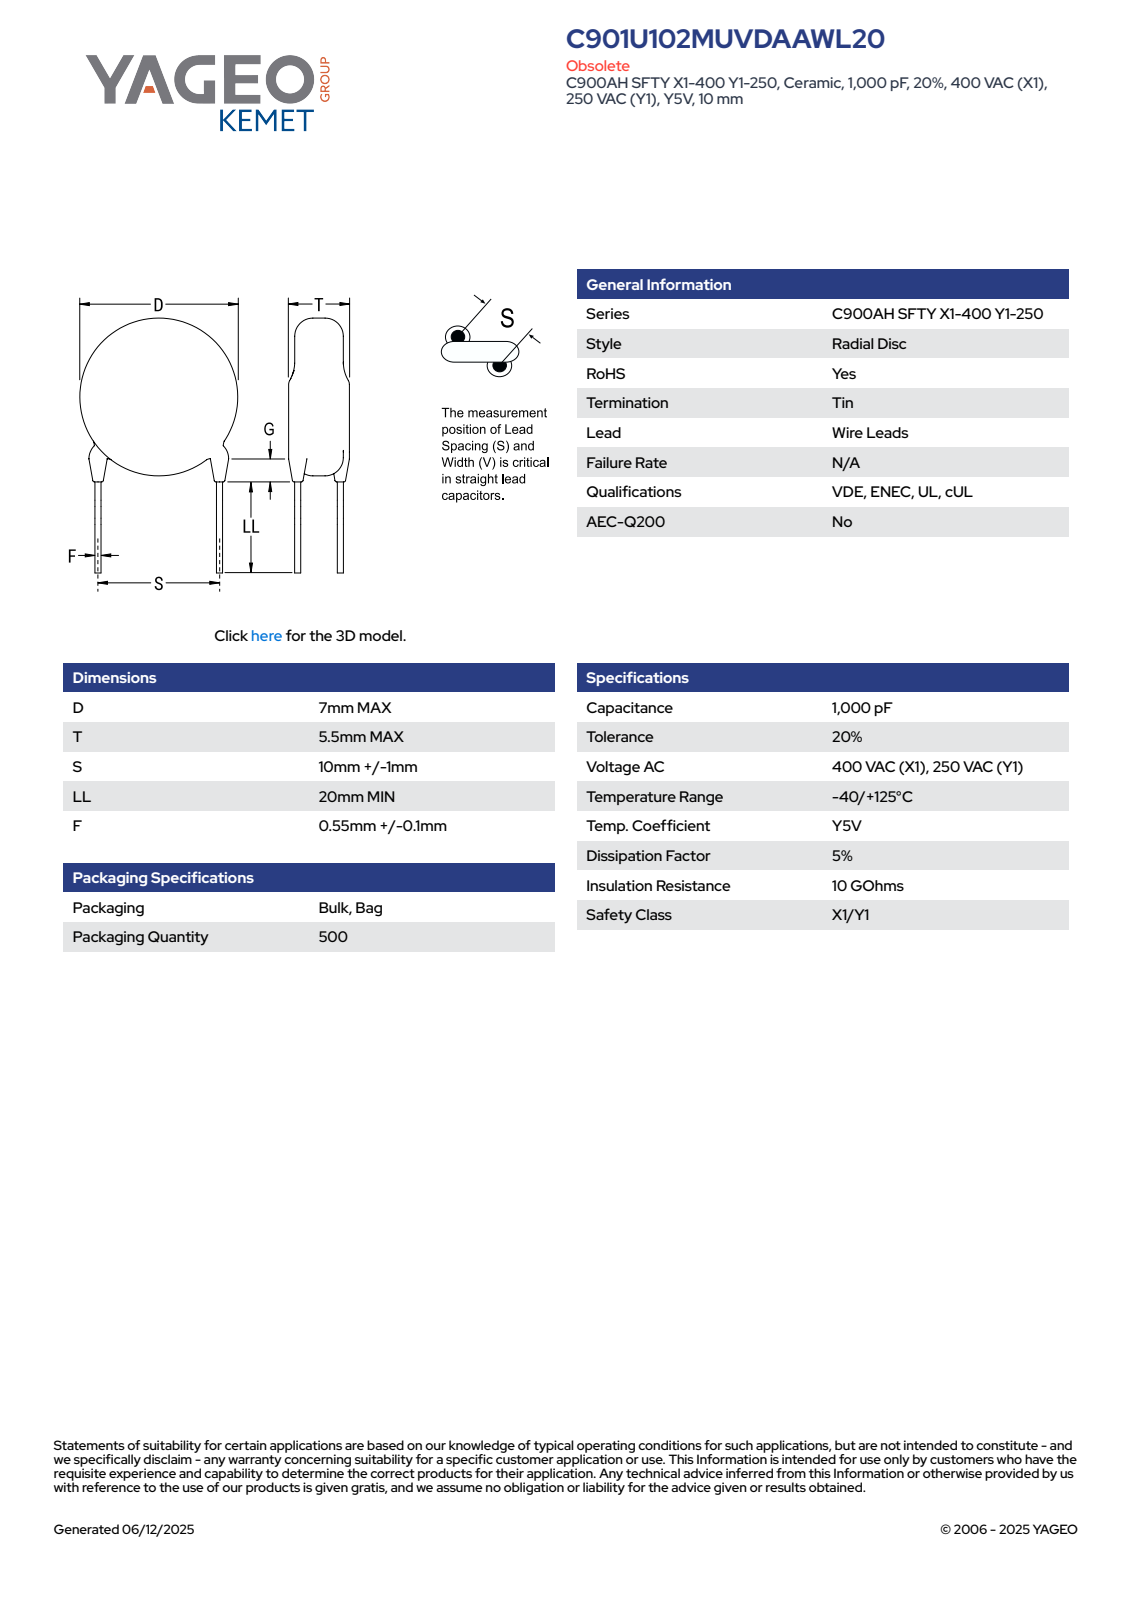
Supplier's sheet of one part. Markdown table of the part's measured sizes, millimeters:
| quantity | value |
| --- | --- |
| part name | CCD_STC900_D7T5.5S10LL20F0.65G3 |
| STEP written by | SolidWorks 2014 (AUTOMOTIVE_DESIGN) |
| units | millimeters |
| bodies | 4 solids, 83 faces (61 planar, 6 cylindrical, 16 other) |
| overall size | 27.44 × 9.77 × 5.5 |
| volume | 222 mm³ |
| surface area | 280 mm² |
| round bosses / shafts (diameter × count) | 0.65 × 2, 7 × 1 |
| main face-to-face distances | 5.5, 0.81, 24.34, 23.53, 3.3, 1.67, 3.52, 2.4, 2.49, 1.32 |
